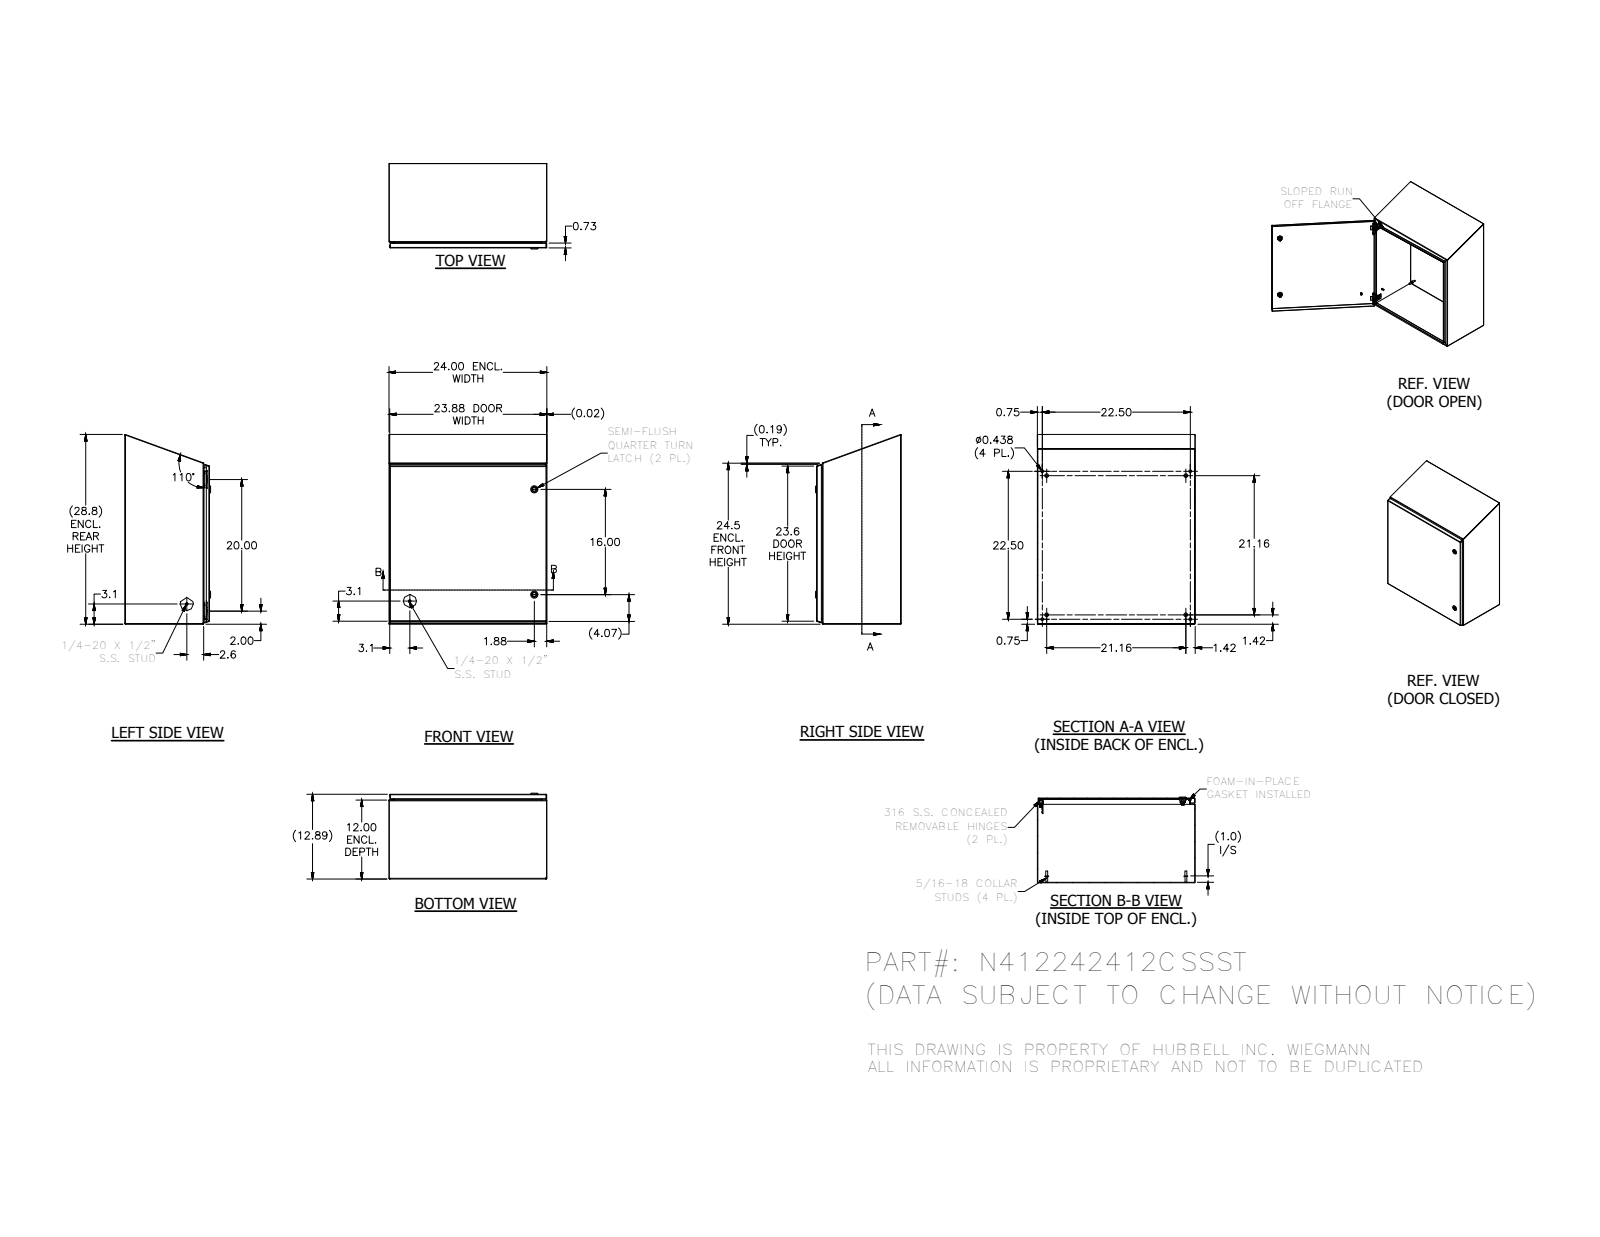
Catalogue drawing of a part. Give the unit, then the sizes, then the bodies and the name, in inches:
Units: inches
Overall size (bounding box): 28.847 × 24 × 13.044
Round holes (diameter × count): ⌀0.093 ×4, ⌀0.152 ×4, ⌀0.167 ×4, ⌀0.172 ×4, ⌀0.187 ×4, ⌀0.437 ×4, ⌀0.156 ×3, ⌀0.197 ×2, ⌀0.315 ×2, ⌀0.394 ×2, ⌀0.402 ×2, ⌀0.634 ×2
Round bosses / shafts (diameter × count): ⌀0.25 ×10, ⌀0.563 ×4, ⌀0.36 ×4, ⌀0.32 ×4, ⌀0.3 ×4, ⌀0.275 ×4, ⌀0.256 ×4, ⌀0.164 ×4
Partial cylindrical surfaces — rounded edges, fillets, slot ends (radius × count): R0.031 ×29, R0.05 ×26, R0.02 ×24, R0.105 ×19, R0.016 ×18, R0.125 ×16, R0.032 ×8, R0.177 ×6
Main face-to-face distances: 0.074, 12.813, 23.926, 12.887, 12.739, 23.852, 24, 11.926, 0.887, 0.813
Hole centre spacings: 20, 22.5, 22.8, 0.5, 0.656, 0.66, 0.952, 1.307
Volume: 200.4 in³ · Surface area: 5 440 in²
Bodies: 44 solids, 1722 faces (709 planar, 604 cylindrical, 409 other)
Part name (STEP PRODUCT): N412242412CSSST
STEP written by: SolidWorks 2018 (AUTOMOTIVE_DESIGN)
